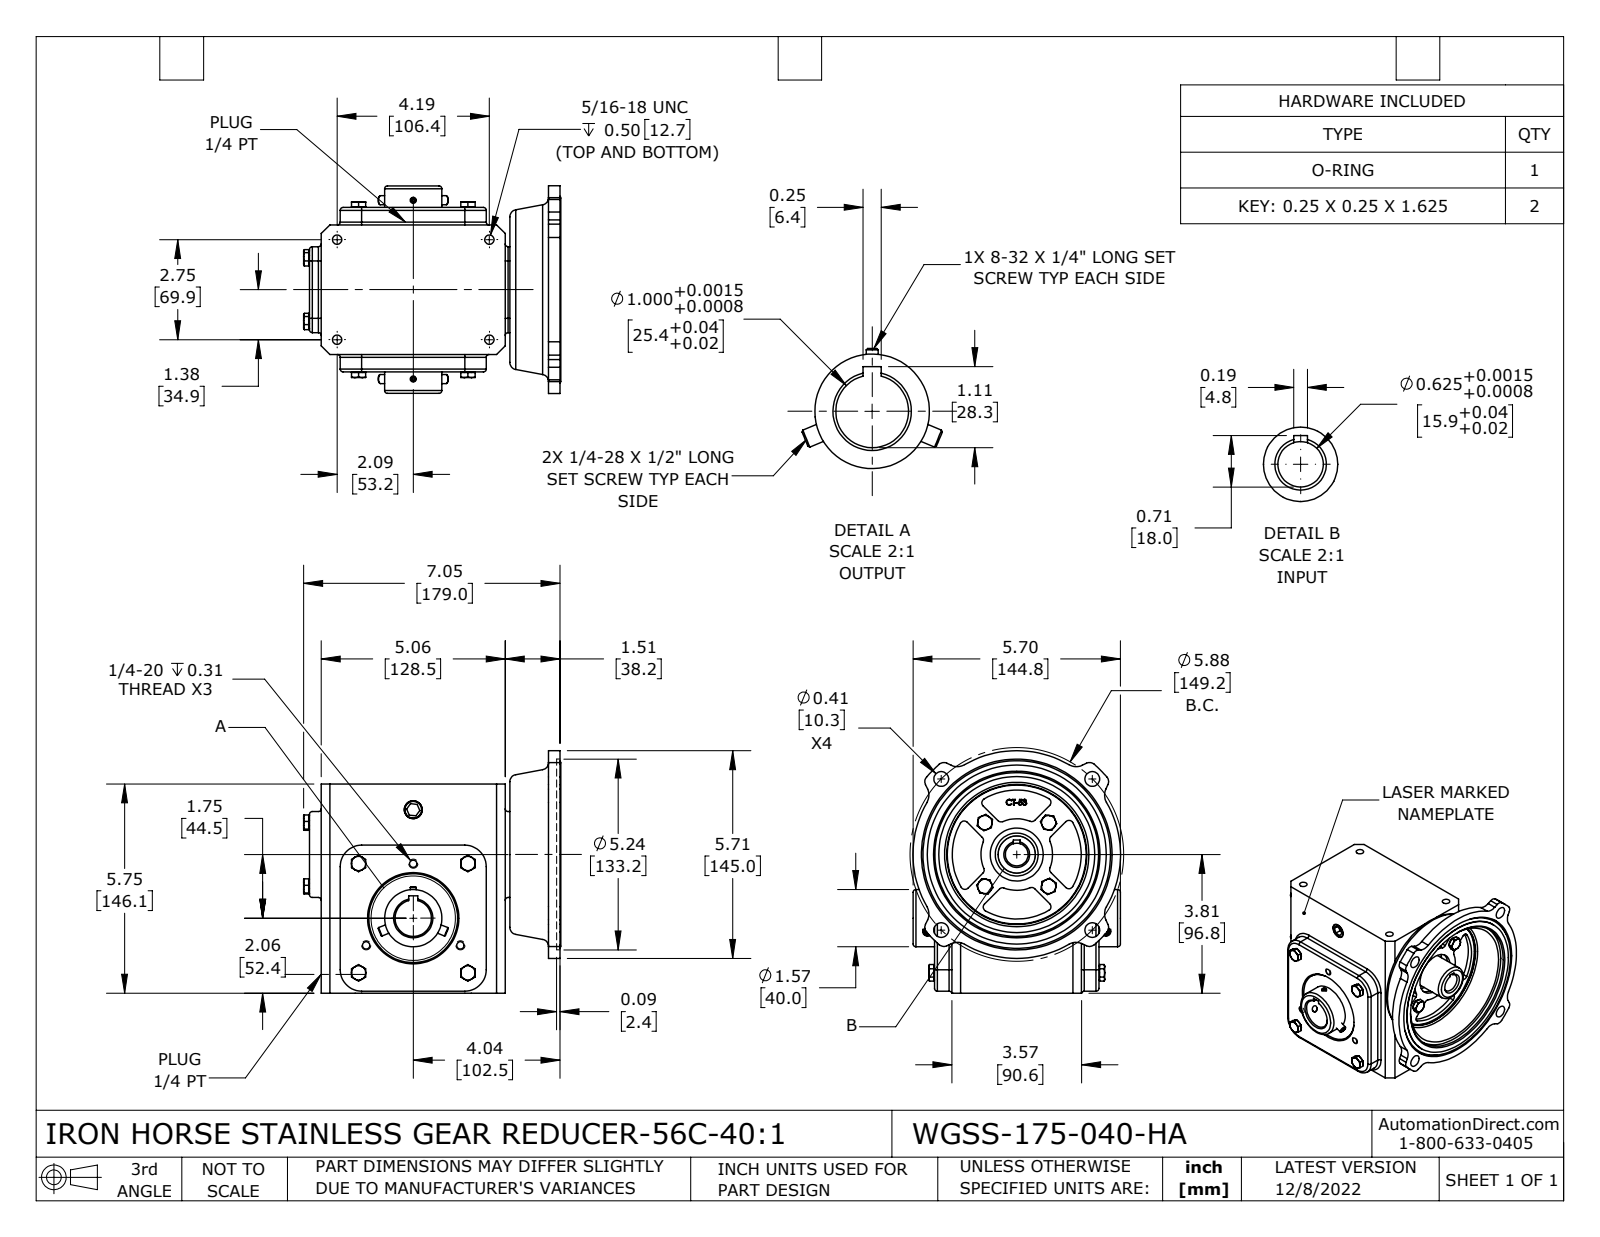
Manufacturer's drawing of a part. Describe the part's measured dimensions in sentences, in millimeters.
The part is named "WGSS-175-040-HA". Its 3-D file was written by "SolidWorks 2021 (CONFIG_CONTROL_DESIGN)". It is 7 solids with 891 faces: 390 planar, 231 cylindrical and 270 other. Overall it measures 179.6 by 170 by 145 millimeters. Its volume is 2 081 000 cubic millimeters and its surface area 181 300 square millimeters. Round holes: 4 of diameter 5.4, 4 of diameter 6.5, 4 of diameter 10.3, 3 of diameter 5.1, 2 of diameter 3.5, 1 of diameter 15.9, 1 of diameter 22, 1 of diameter 25.4, 1 of diameter 28, 1 of diameter 37, 1 of diameter 40, 1 of diameter 97. Round bosses or shafts: 8 of diameter 10, 4 of diameter 6.4, 2 of diameter 4.2, 1 of diameter 125, 1 of diameter 62, 1 of diameter 40, 1 of diameter 30. Partial cylindrical surfaces (rounded edges, fillets, slot ends): 28 of radius 2, 16 of radius 3, 12 of radius 10, 8 of radius 5, 4 of radius 15, 1 of radius 25, 1 of radius 45, 1 of radius 72.5. The main face-to-face distances are 12.2, 102.6, 146.1, 128.5, 4, 90.4, 114.8, 8, 166.8, 38.3. The hole center spacings are 59.9, 74.6, 105.5, 38, 65.8, 124.8, 69.9, 106.4.
